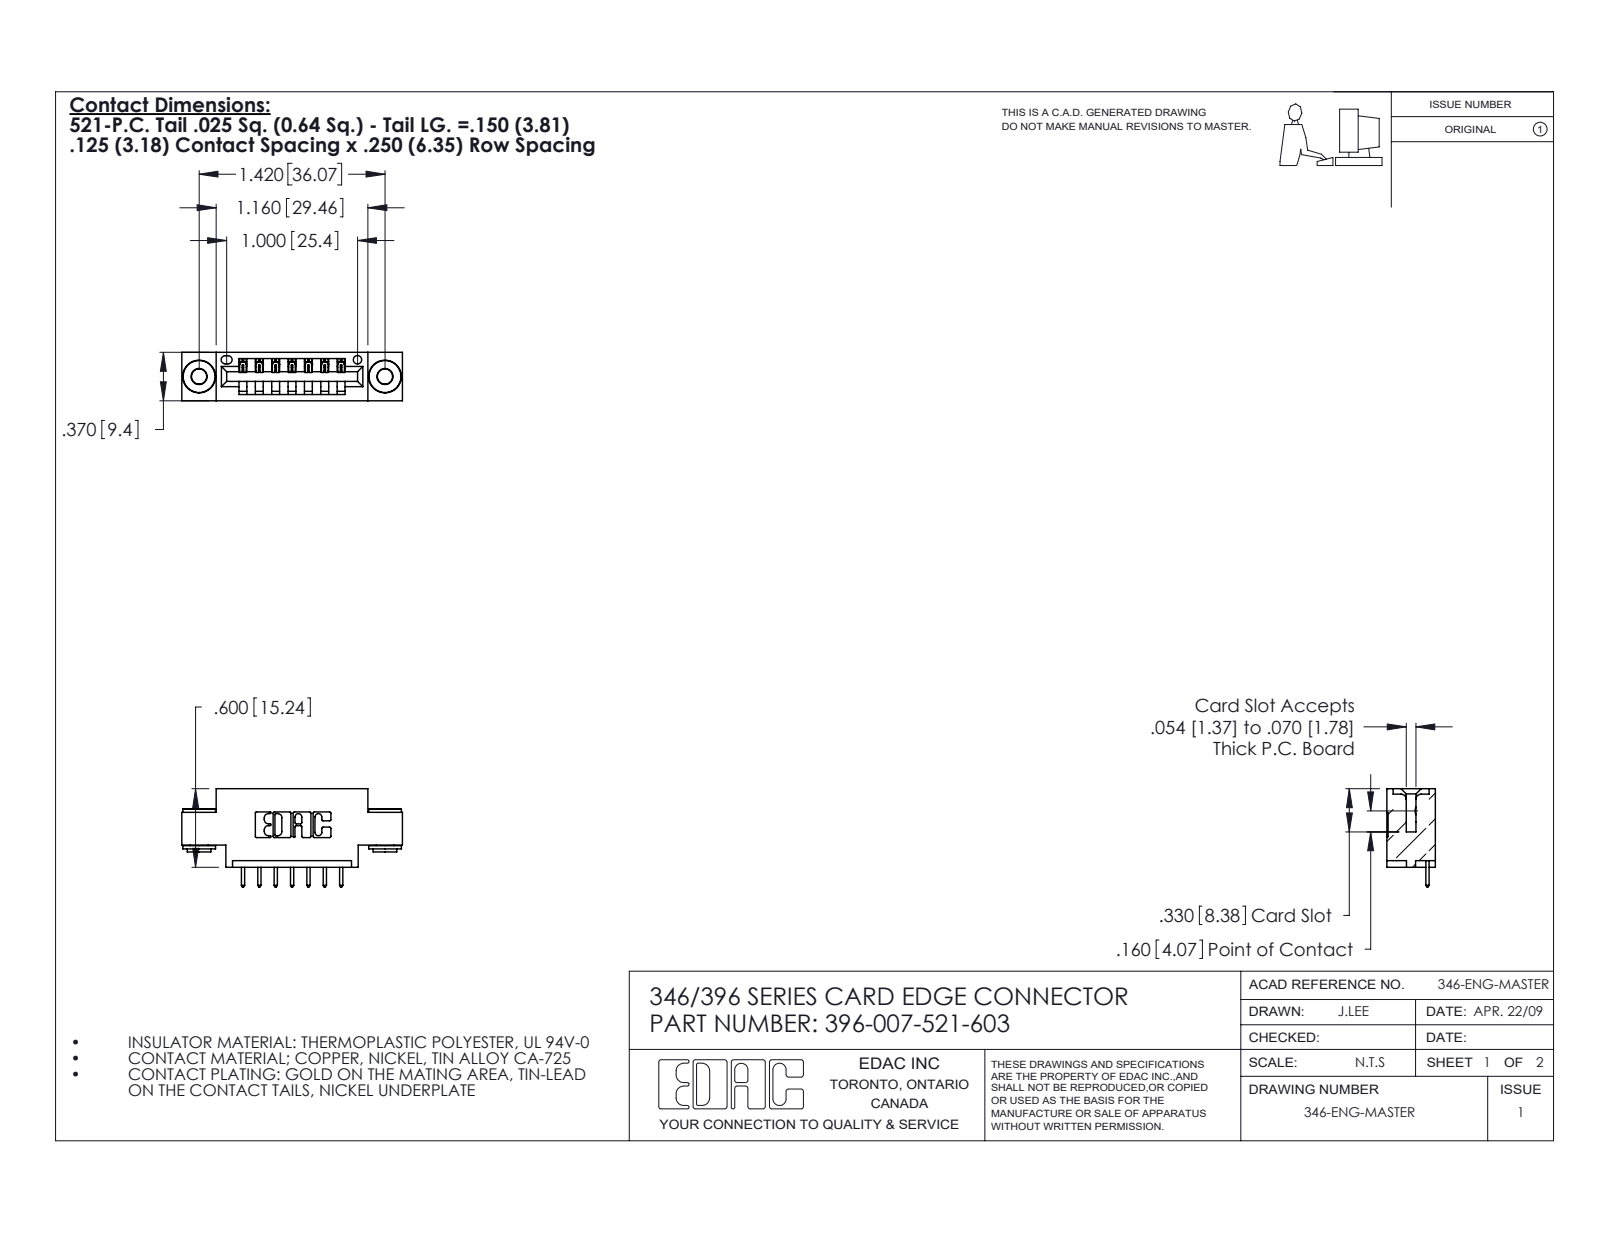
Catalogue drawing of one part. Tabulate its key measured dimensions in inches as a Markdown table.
| quantity | value |
| --- | --- |
| part name | 345-250-002_345-250-002-102; 346 Part_0.170 Offset - 0.156 Dia-TH; 345-292-001_345-293-121; 396-007-521-603 |
| STEP written by | SolidWorks 2020 (CONFIG_CONTROL_DESIGN) |
| units | inches |
| bodies | 10 solids, 584 faces (384 planar, 192 cylindrical, 8 other) |
| overall size | 1.685 × 0.75 × 0.37 |
| volume | 0.225 in³ |
| surface area | 7.064 in² |
| round holes (diameter × count) | 0.116 × 2, 0.156 × 2, 0.064 × 1 |
| round bosses / shafts (diameter × count) | 0.25 × 2, 0.18 × 2, 0.136 × 2 |
| partial cylindrical surfaces (radius × count) | 0.01 × 22, 0.006 × 14, 0.01 × 14, 0.007 × 6, 0.031 × 6, 0.026 × 3, 0.031 × 2, 0.04 × 2 |
| main face-to-face distances | 0.25, 0.37, 0.048, 0.322, 0.025, 0.222, 0.148, 0.1, 0.174, 0.125 |
| hole center spacings | 0.246, 1.217, 1.42 |
